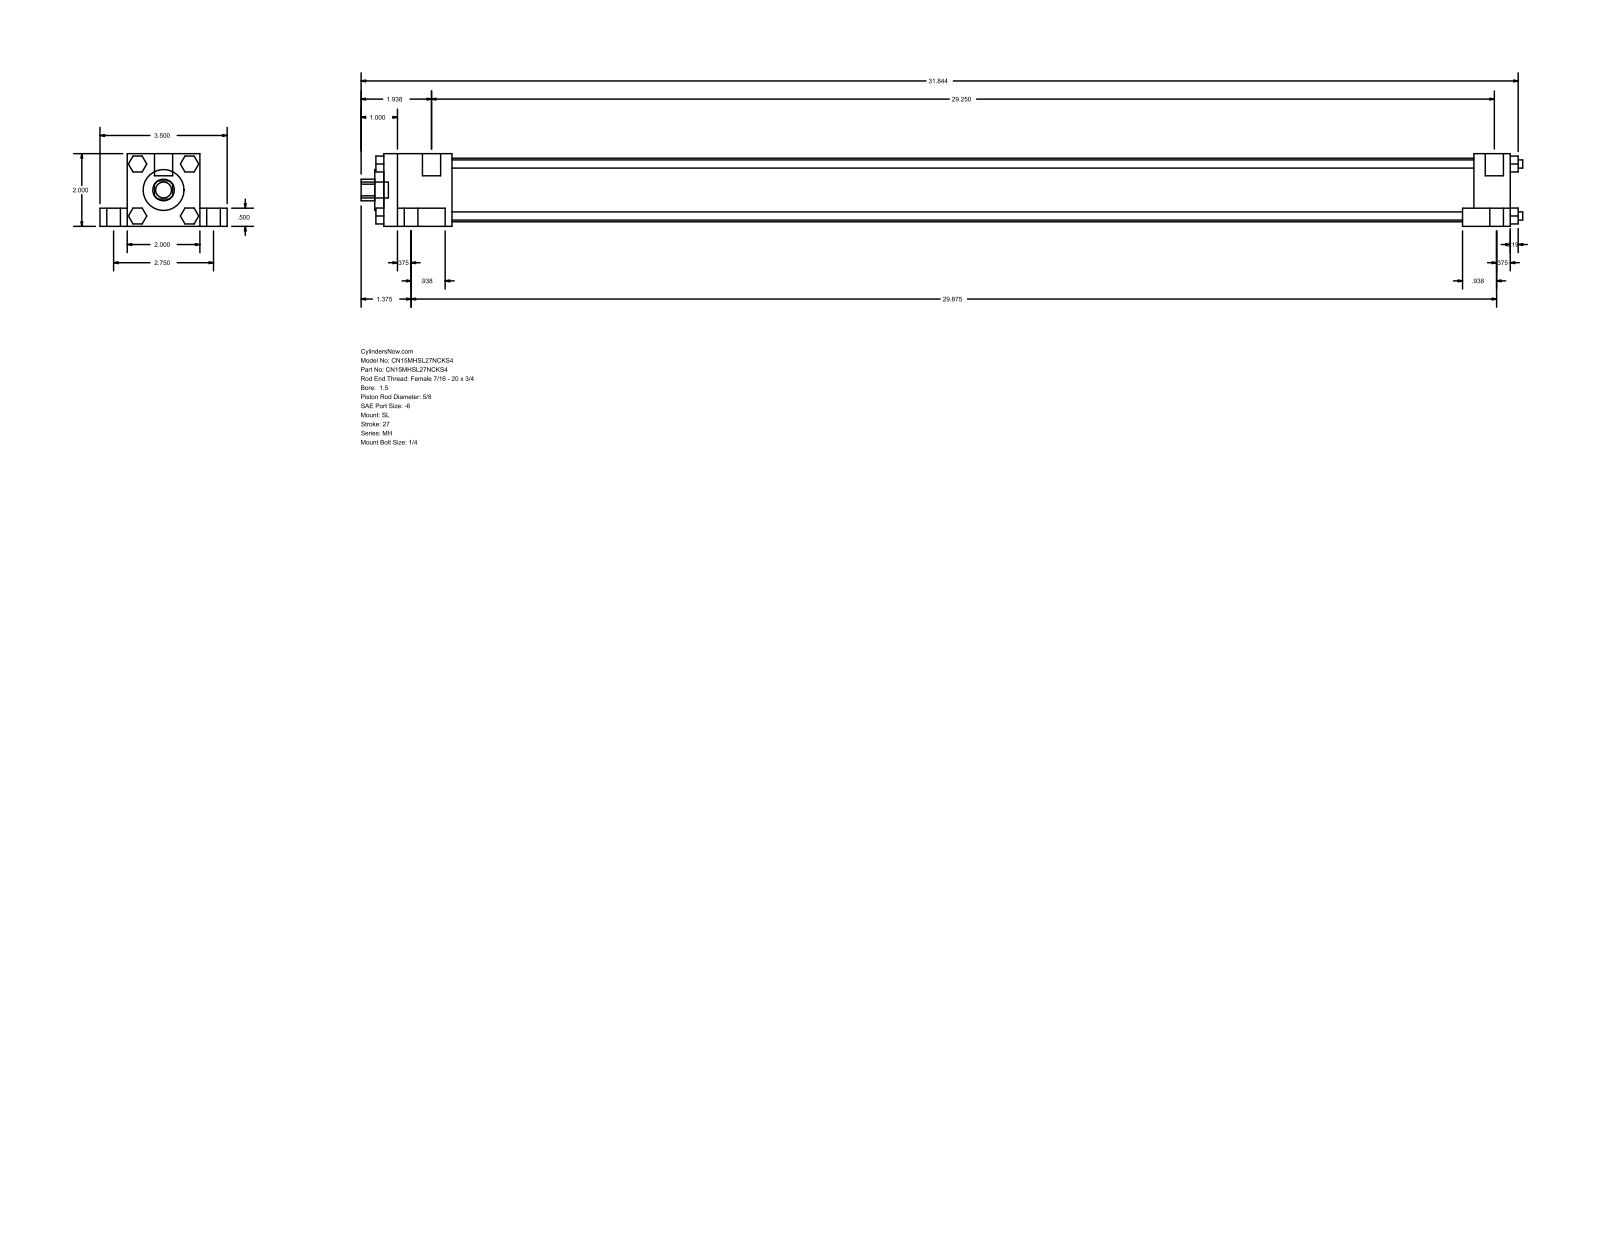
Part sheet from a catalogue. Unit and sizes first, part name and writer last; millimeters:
Units: millimetres
Overall size (bounding box): 812.01 × 88.9 × 50.8
Round holes (diameter × count): ⌀15.88 ×1, ⌀28.57 ×1, ⌀44.45 ×1
Round bosses / shafts (diameter × count): ⌀15.88 ×4, ⌀9.53 ×4, ⌀5.71 ×4, ⌀5.56 ×4, ⌀12.7 ×2, ⌀11.11 ×1
Partial cylindrical surfaces — rounded edges, fillets, slot ends (radius × count): R7.54 ×1
Main face-to-face distances: 50.8, 38.1, 19.05, 12.7, 69.85, 787.39, 9.52, 762, 25.39, 47.62
Bodies: 0 solids, 148 faces (112 planar, 36 cylindrical, 0 other)
Part name (STEP PRODUCT): MH_SL__0150_0.625
STEP written by: GSSL Pune (CONFIG_CONTROL_DESIGN)
